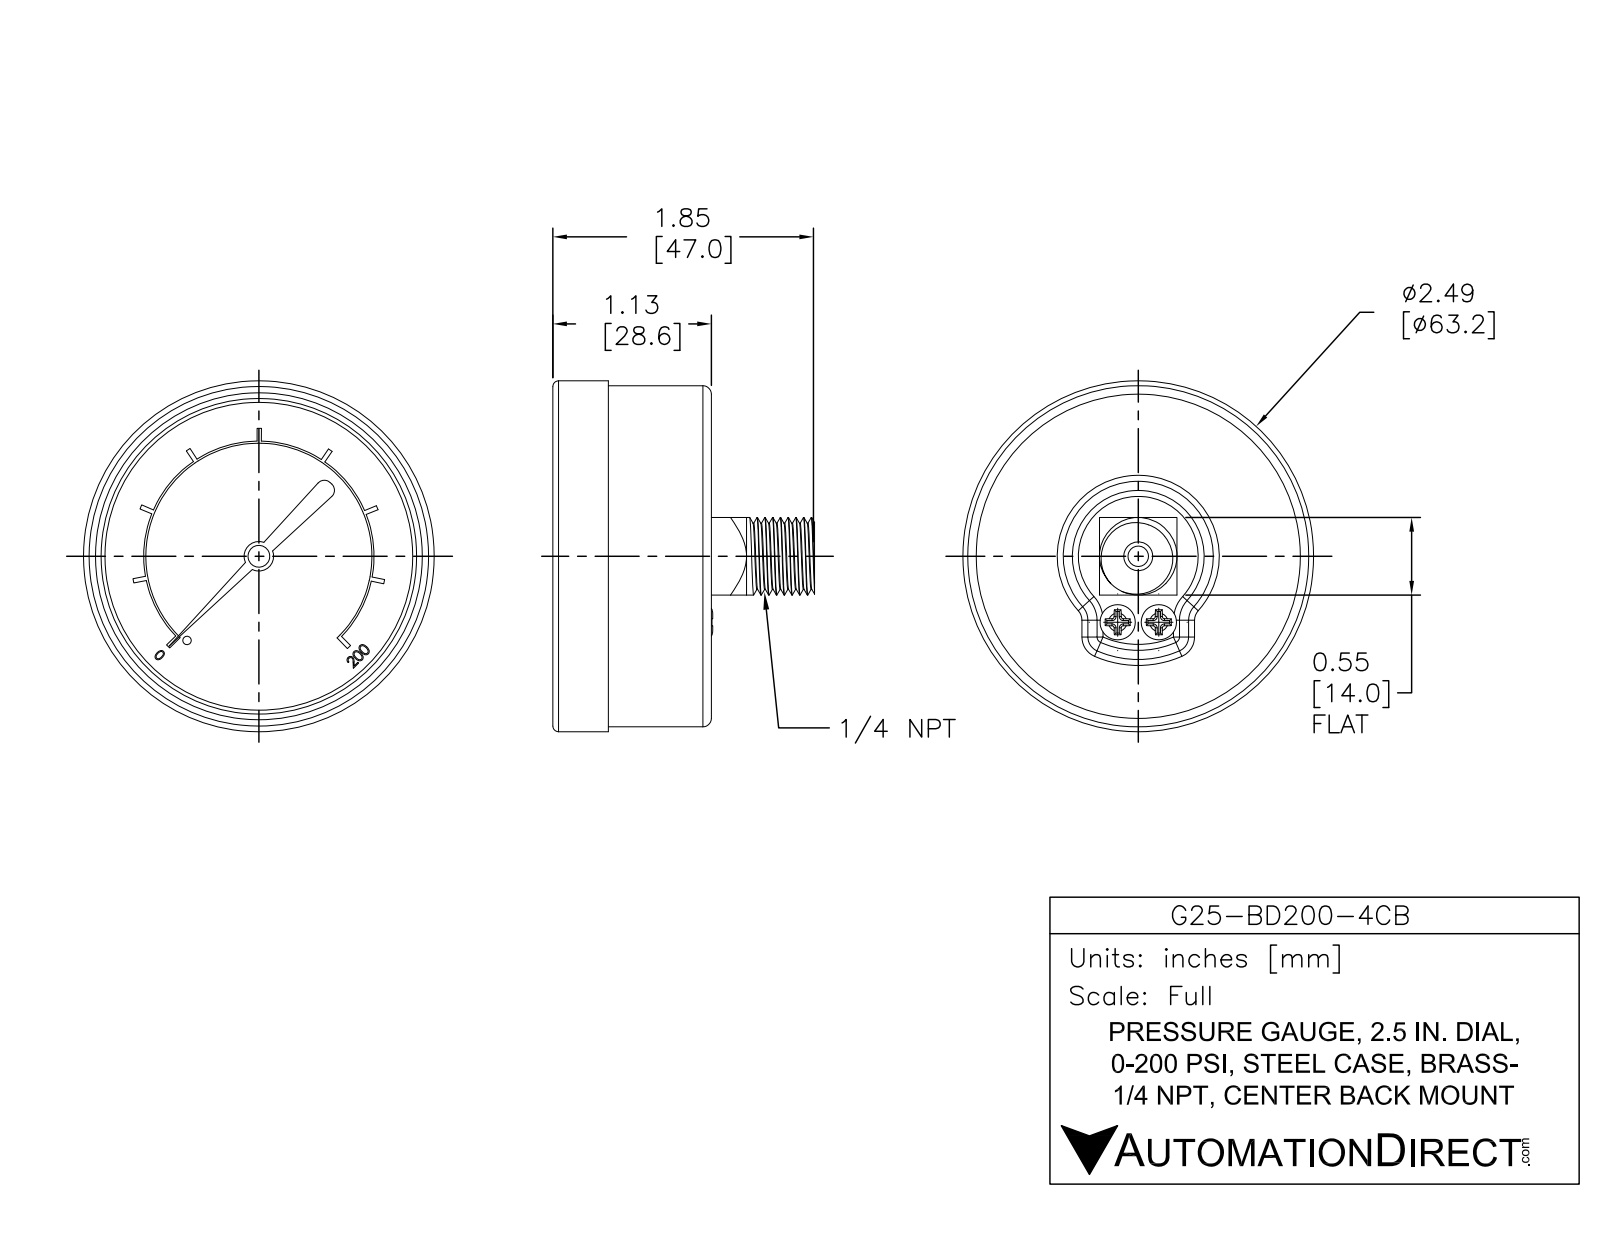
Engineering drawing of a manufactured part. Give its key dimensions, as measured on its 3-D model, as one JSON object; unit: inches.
{"part_name": "G25-BD200-4CB", "step_written_by": "SolidWorks 2021 (AUTOMOTIVE_DESIGN)", "units": "inches", "bodies": {"solids": 1, "faces": 205, "planar": 103, "cylindrical": 32, "other": 70}, "overall_size": [2.49, 2.49, 1.858], "volume_in3": 4.301, "surface_area_in2": 22.47, "round_holes": [[0.145, 1], [2.185, 1]], "round_bosses_or_shafts": [[0.25, 2], [2.49, 1], [2.421, 1], [0.55, 1], [0.178, 1], [0.099, 1], [0.04, 1]], "partial_cylinders_radius": [[0.06, 4], [0.03, 2], [0.115, 1], [0.813, 1], [0.823, 1]], "face_to_face_distances": [0.835, 0.1, 1.125, 0.29, 0.735, 1.025, 0.731, 0.631, 0.104, 0.394]}
